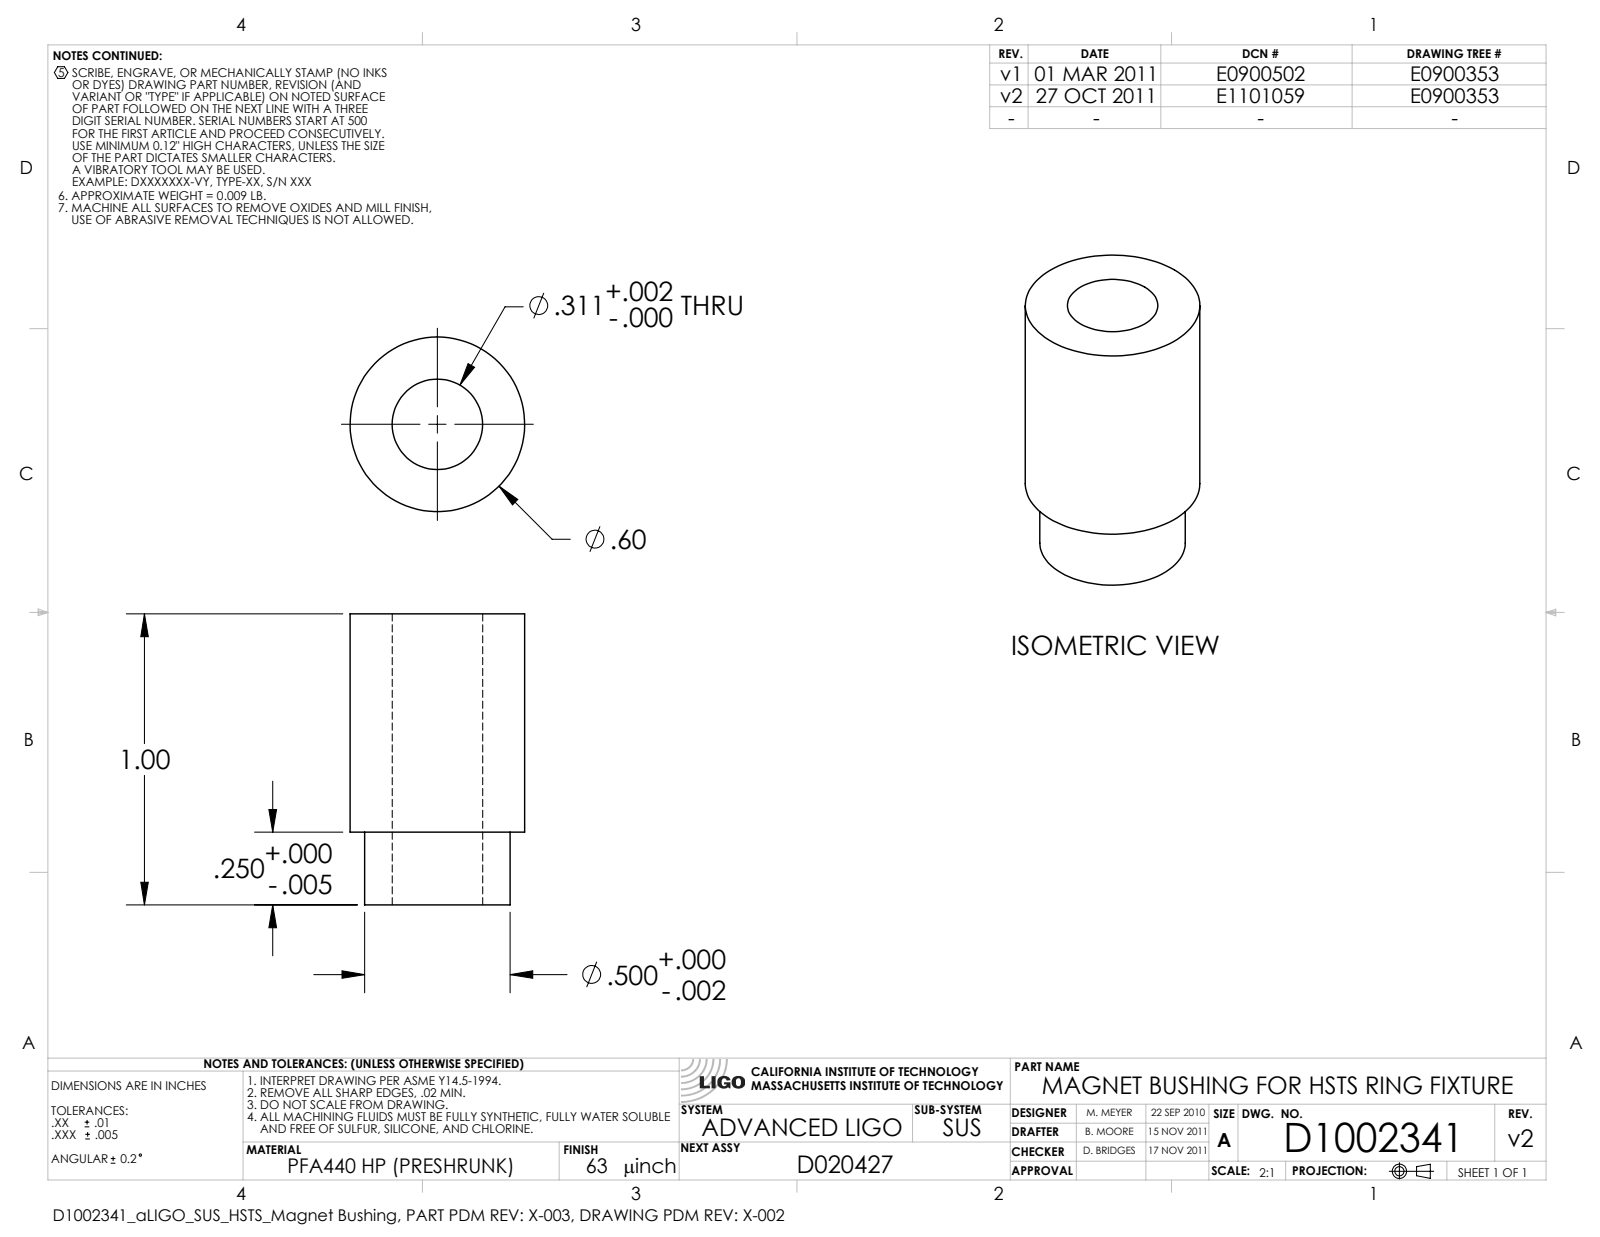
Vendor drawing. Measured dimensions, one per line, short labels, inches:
name: D1002341-v2_aLIGO_SUS_HSTS_Magnet Bushing
written by: SolidWorks 2012 (AUTOMOTIVE_DESIGN)
unit: in
bodies: 1 solid, 9 faces (3 planar, 6 cylindrical, 0 other)
size: 1 × 0.6 × 0.6
volume: 0.185 in³; area: 3.197 in²
holes: 1× ⌀0.311
bosses: 1× ⌀0.6, 1× ⌀0.5
face distances: 1, 0.25, 0.75
